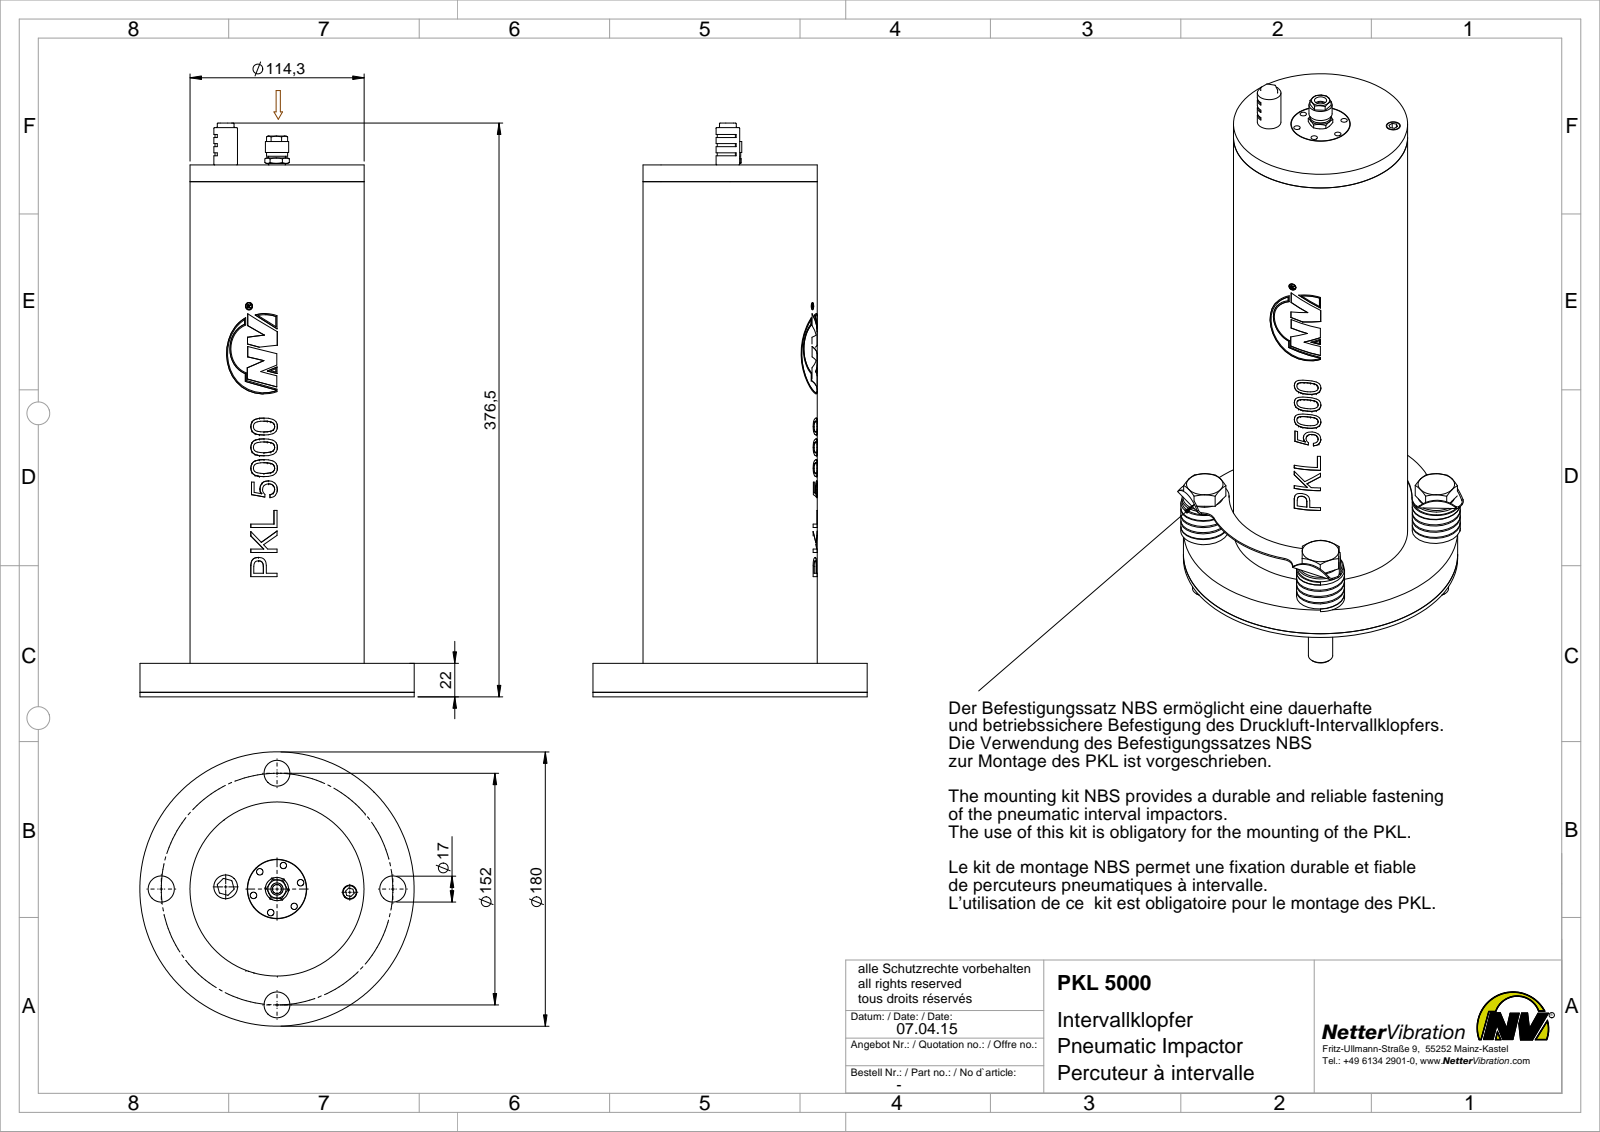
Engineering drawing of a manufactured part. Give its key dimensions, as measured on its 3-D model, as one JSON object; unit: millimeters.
{"part_name": "PKL 5000", "step_written_by": "SolidWorks 2015 (AUTOMOTIVE_DESIGN)", "units": "millimeters", "bodies": {"solids": 12, "faces": 745, "planar": 243, "cylindrical": 191, "other": 311}, "overall_size": [402, 180, 180], "volume_mm3": 4073000, "surface_area_mm2": 352640, "round_holes": [[4.2, 6], [17, 4], [8.57, 3], [6, 1], [6.81, 1], [7, 1], [8, 1], [13.4, 1], [34.4, 1], [38.5, 1], [41.5, 1], [70, 1]], "round_bosses_or_shafts": [[31.5, 4], [30, 4], [24, 4], [16, 4], [180, 1], [114.3, 1], [108.2, 1], [72, 1]], "partial_cylinders_radius": [[0.5, 18], [1, 8], [2, 8], [17, 8], [18.5, 8], [8, 4], [7, 1], [57.14, 1]], "face_to_face_distances": [3, 22, 19, 316, 338, 335, 11, 327, 1, 321], "hole_center_spacings": [16, 27.71, 76, 107.48, 32, 15.99, 16.01, 60.45]}
